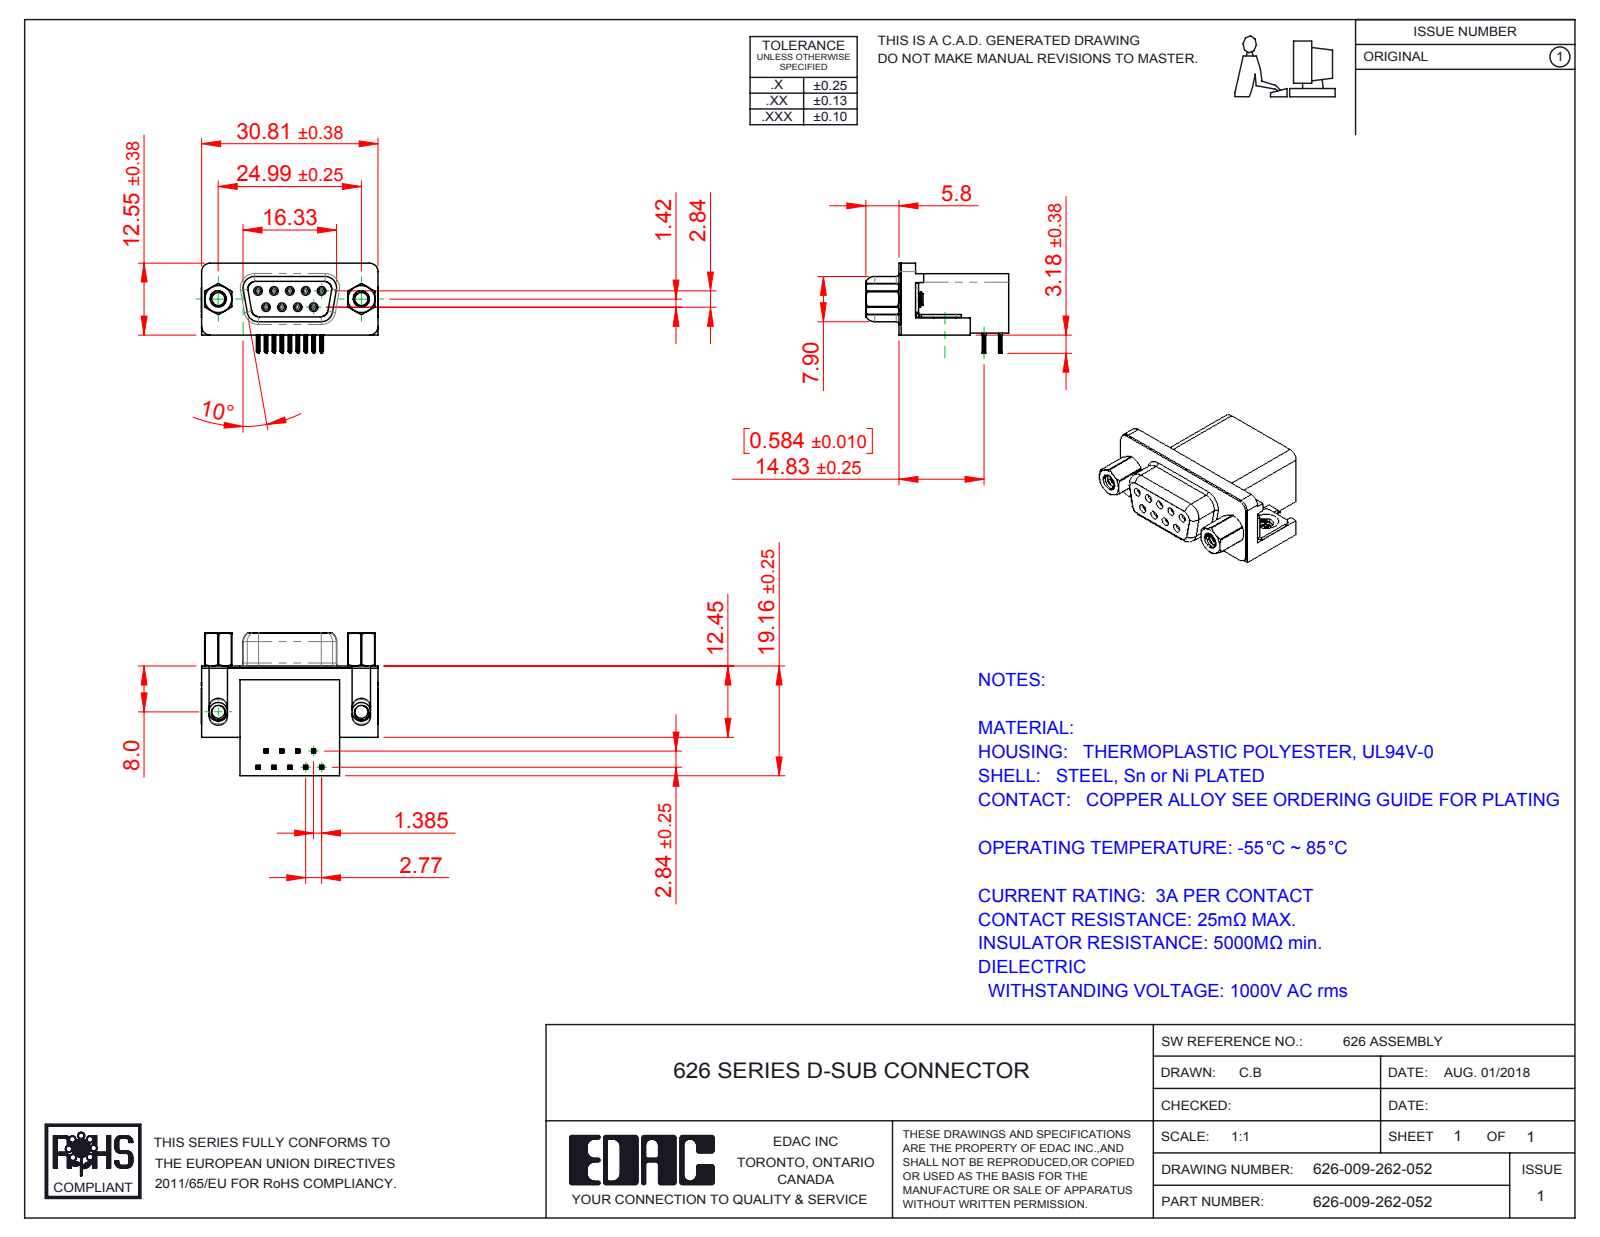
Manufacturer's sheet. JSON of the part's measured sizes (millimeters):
{"part_name": "626 Housing_9 Socket; 626 Shell_9 Socket; 626 Contact Bottom; 626 Contact Top (+3 more)", "step_written_by": "SolidWorks 2016 (CONFIG_CONTROL_DESIGN)", "units": "millimeters", "bodies": {"solids": 15, "faces": 1642, "planar": 692, "cylindrical": 462, "other": 488}, "overall_size": [30.89, 24.96, 15.73], "volume_mm3": 5111, "surface_area_mm2": 6032, "round_holes": [[0.8, 9], [0.9, 9], [2.26, 2], [2.29, 2], [4, 2], [4.8, 2], [5, 2]], "round_bosses_or_shafts": [[1.2, 9], [4.9, 2], [3.26, 2], [2.79, 2]], "partial_cylinders_radius": [[0.1, 72], [0.15, 36], [0.35, 18], [1, 18], [0.34, 9], [1.35, 8], [1.6, 8], [1.5, 7]], "face_to_face_distances": [0.4, 10.34, 0.35, 18.76, 19.16, 16.26, 2.9, 2.5, 6.2, 5.8], "hole_center_spacings": [3.16, 2.77, 5.54, 5.03, 5.04, 8.31, 7.48, 7.49]}
